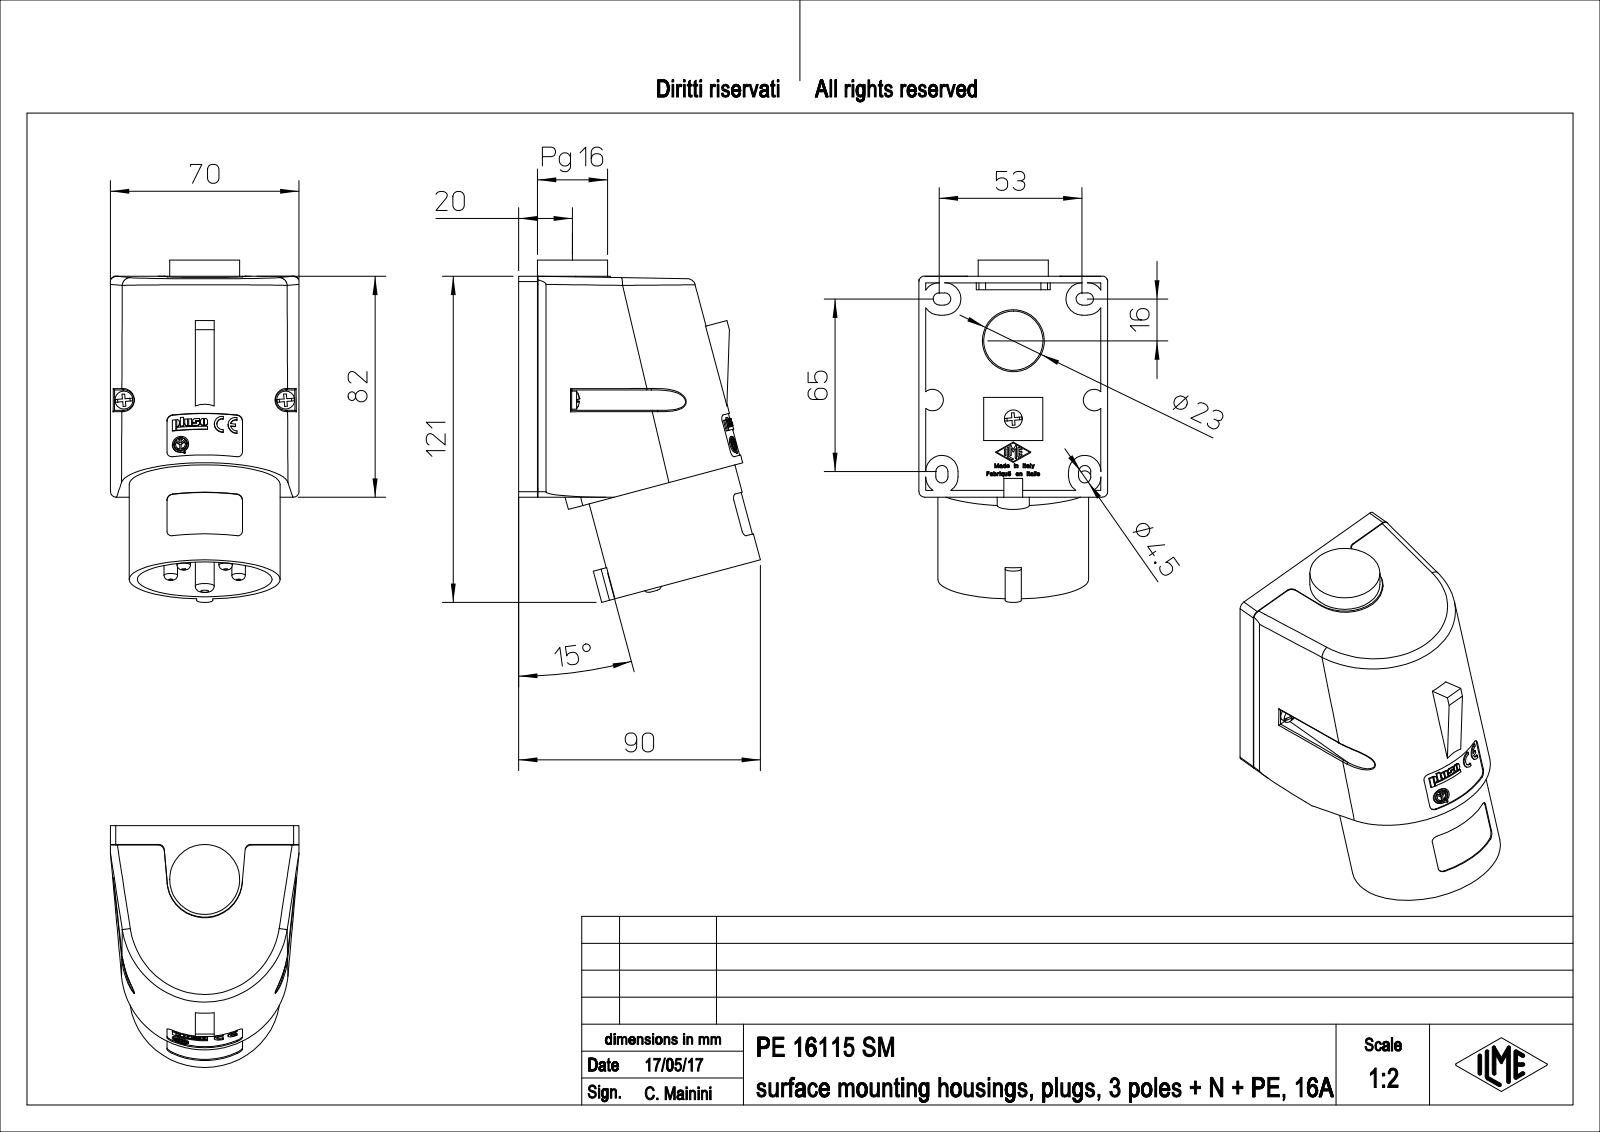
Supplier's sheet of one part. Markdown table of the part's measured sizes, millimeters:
| quantity | value |
| --- | --- |
| part name | PE_16115_SM |
| STEP written by | PTC Creo Elements/Direct Modeling 19.0E 27-Jun-2016 (C) Parametric Technology GmbH (AUTOMOTIVE_DESIGN) |
| units | millimeters |
| bodies | 1 solid, 1845 faces (1561 planar, 188 cylindrical, 96 other) |
| overall size | 127.04 × 89.75 × 70 |
| volume | 341 934 mm³ |
| surface area | 67 379 mm² |
| round holes (diameter × count) | 3.2 × 2, 4.3 × 2, 4.5 × 2, 3 × 1, 5.04 × 1, 21.3 × 1, 23 × 1, 24 × 1, 50 × 1 |
| round bosses / shafts (diameter × count) | 5 × 6, 6.7 × 5, 26 × 2, 56 × 1, 49 × 1, 7 × 1, 6 × 1 |
| partial cylindrical surfaces (radius × count) | 0.25 × 15, 2 × 14, 6 × 13, 0.5 × 9, 0.86 × 9, 2.25 × 8, 4 × 8, 1 × 6 |
| main face-to-face distances | 2.5, 6.2, 3.7, 3.5, 6, 1, 7.2, 7, 82, 3 |
| hole center spacings | 37.2, 60 |
